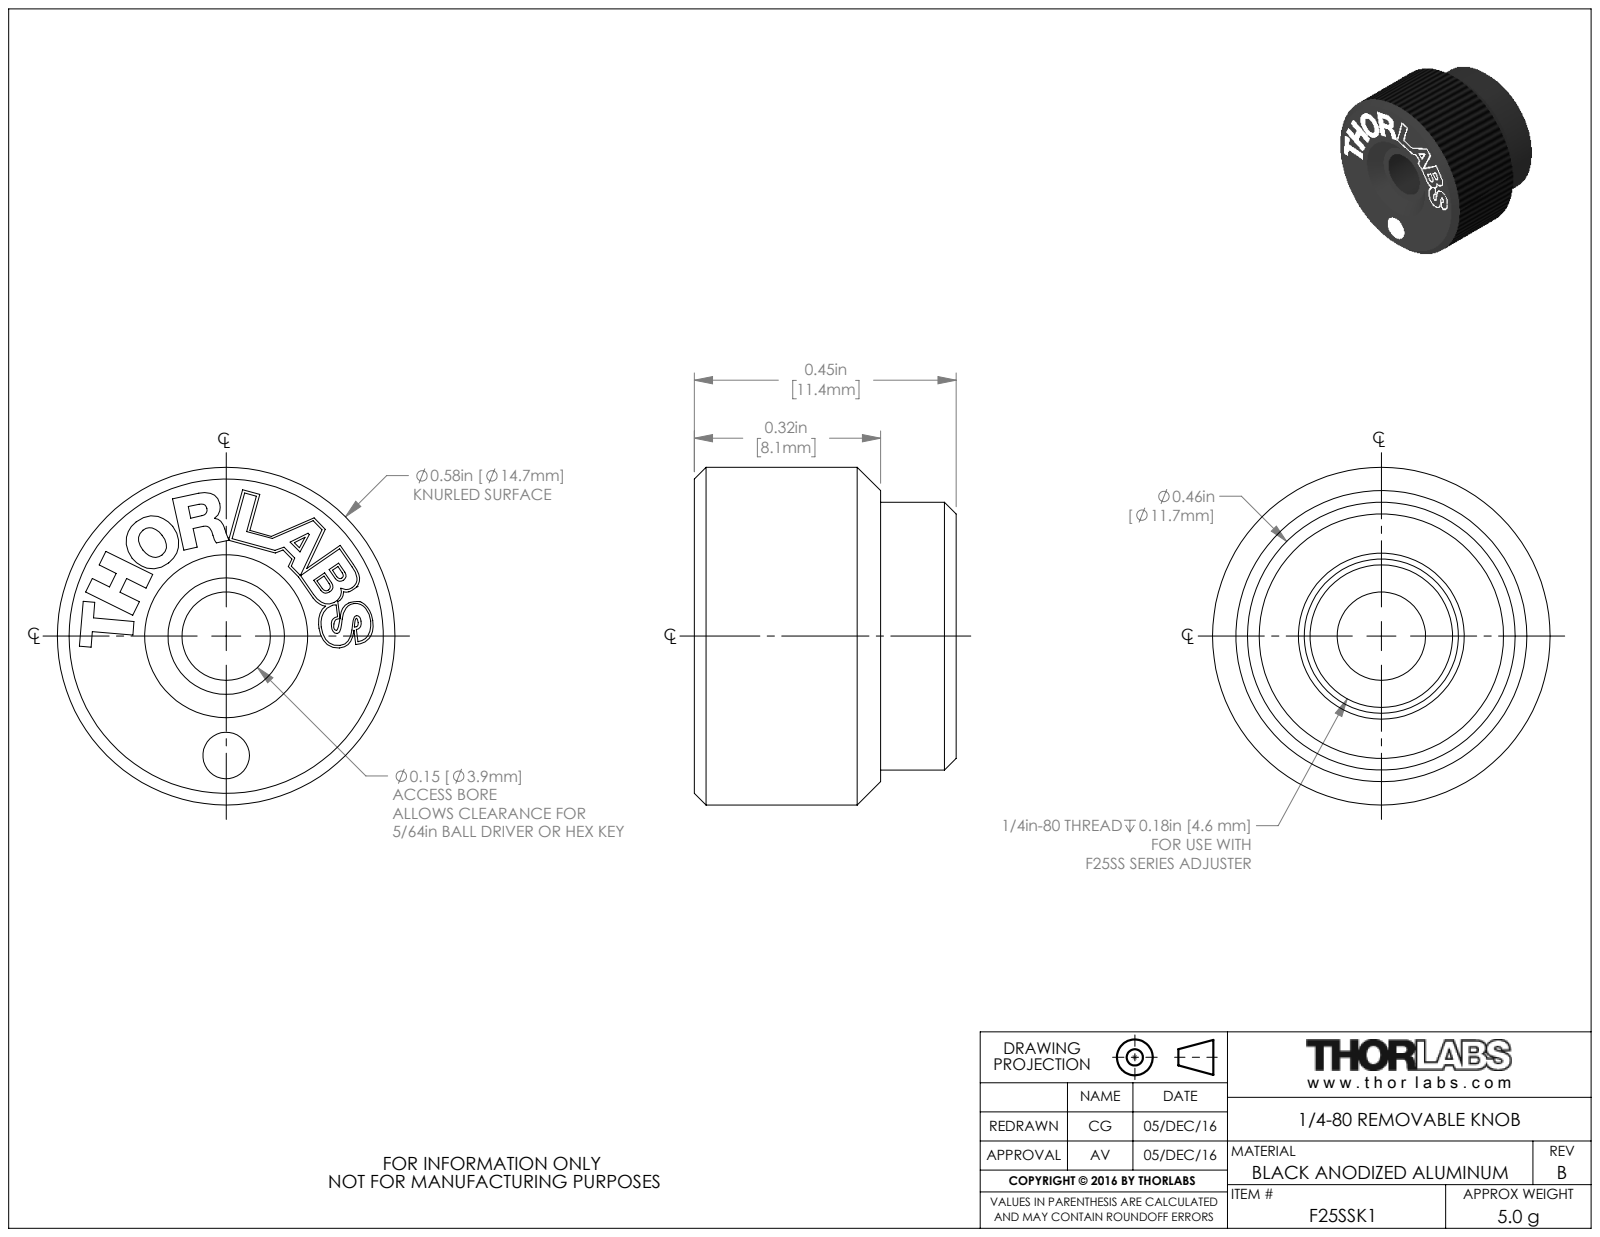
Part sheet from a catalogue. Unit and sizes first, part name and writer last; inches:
Units: inches
Overall size (bounding box): 0.58 × 0.58 × 0.45
Round holes (diameter × count): ⌀0.08 ×1, ⌀0.152 ×1, ⌀0.245 ×1, ⌀0.265 ×1, ⌀0.29 ×1
Round bosses / shafts (diameter × count): ⌀0.58 ×1, ⌀0.46 ×1
Partial cylindrical surfaces — rounded edges, fillets, slot ends (radius × count): R0.014 ×1, R0.047 ×1, R0.059 ×1
Main face-to-face distances: 0.45, 0.27, 0.18, 0.32, 0.05, 0.13, 0.04, 0.31, 0.14, 0.04
Hole centre spacings: 0.205
Volume: 0.088 in³ · Surface area: 1.48 in²
Bodies: 1 solid, 208 faces (118 planar, 19 cylindrical, 71 other)
Part name (STEP PRODUCT): 8548-E0W
STEP written by: SolidWorks 2016 (AUTOMOTIVE_DESIGN)
